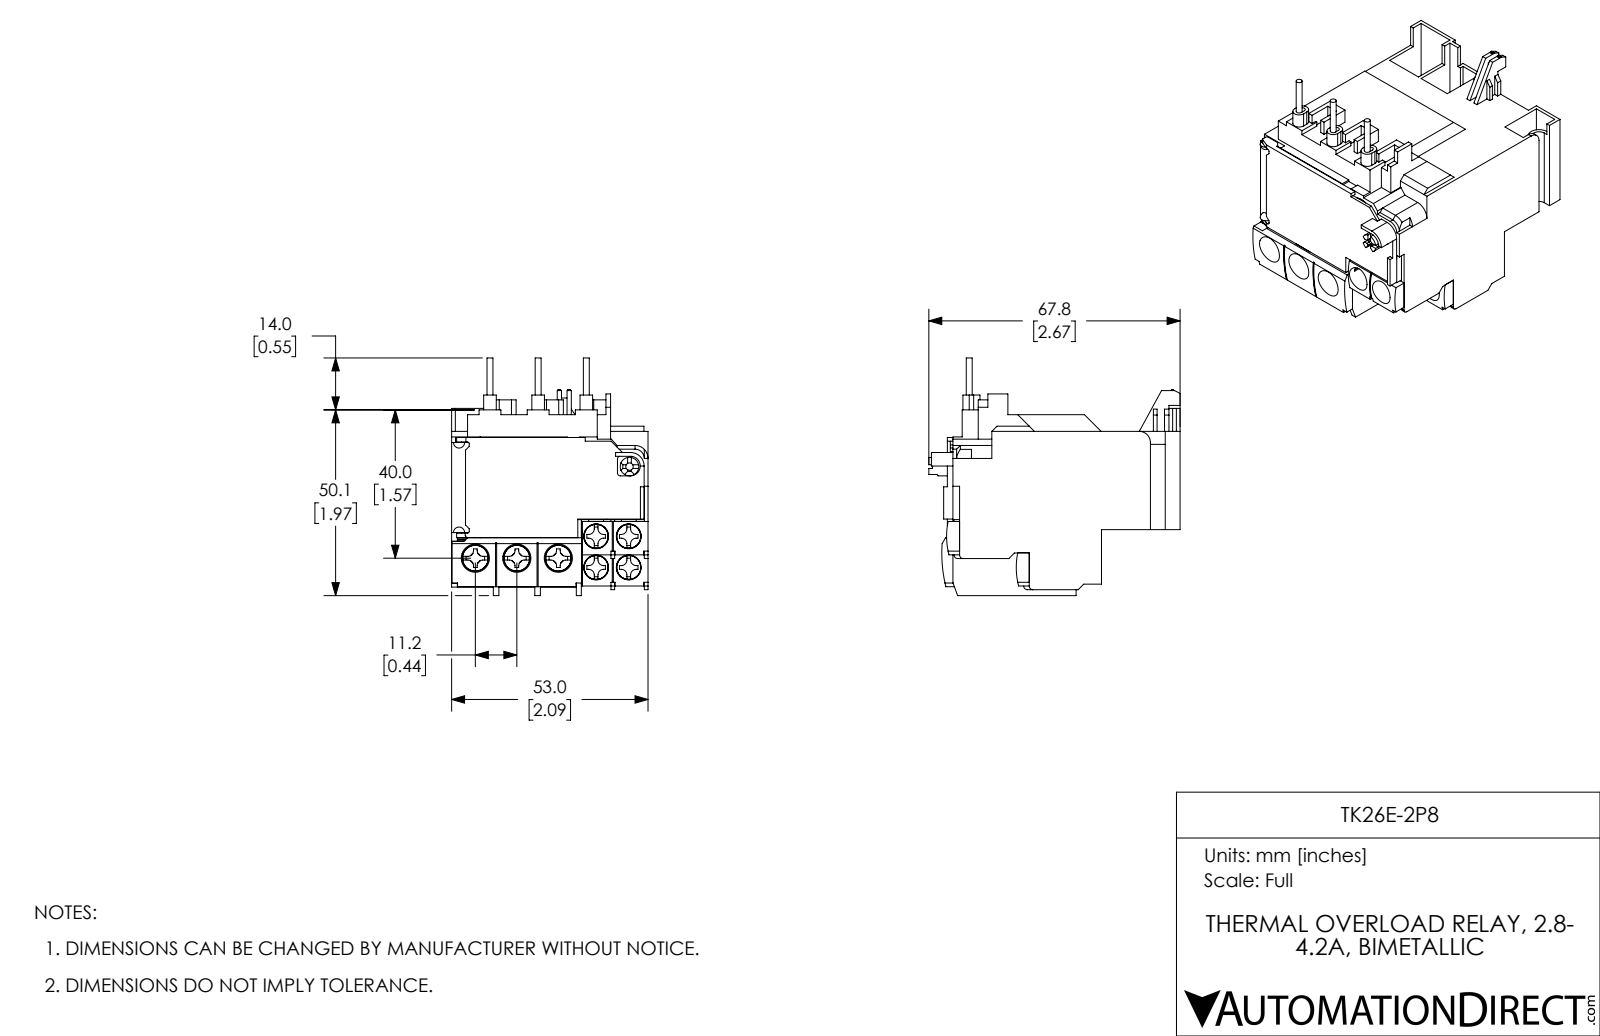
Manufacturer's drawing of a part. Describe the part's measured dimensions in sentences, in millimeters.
The part is named "TK26E-2P8". Its 3-D file was written by "SolidWorks 2017 (AUTOMOTIVE_DESIGN)". It is 38 solids with 1480 faces: 1225 planar, 220 cylindrical and 35 other. Overall it measures 67.8 by 64.1 by 53 millimeters. Its volume is 99 940 cubic millimeters and its surface area 38 810 square millimeters. Round holes: 4 of diameter 3.5, 4 of diameter 3.6, 4 of diameter 6.7, 3 of diameter 4, 3 of diameter 4.1, 3 of diameter 7.6, 1 of diameter 1, 1 of diameter 2, 1 of diameter 5, 1 of diameter 11. Round bosses or shafts: 4 of diameter 6.6, 3 of diameter 1.6, 1 of diameter 6. Partial cylindrical surfaces (rounded edges, fillets, slot ends): 28 of radius 1.5, 8 of radius 1, 6 of radius 0.5, 6 of radius 1.7, 5 of radius 0.8, 4 of radius 1.2, 4 of radius 4.3, 3 of radius 4.8. The main face-to-face distances are 1, 9, 1.5, 12, 53, 2, 10, 11, 8.7, 0.7. The hole center spacings are 8.4, 8.8, 11.2, 12.2, 9.6, 10.5, 11.8, 18.8.
